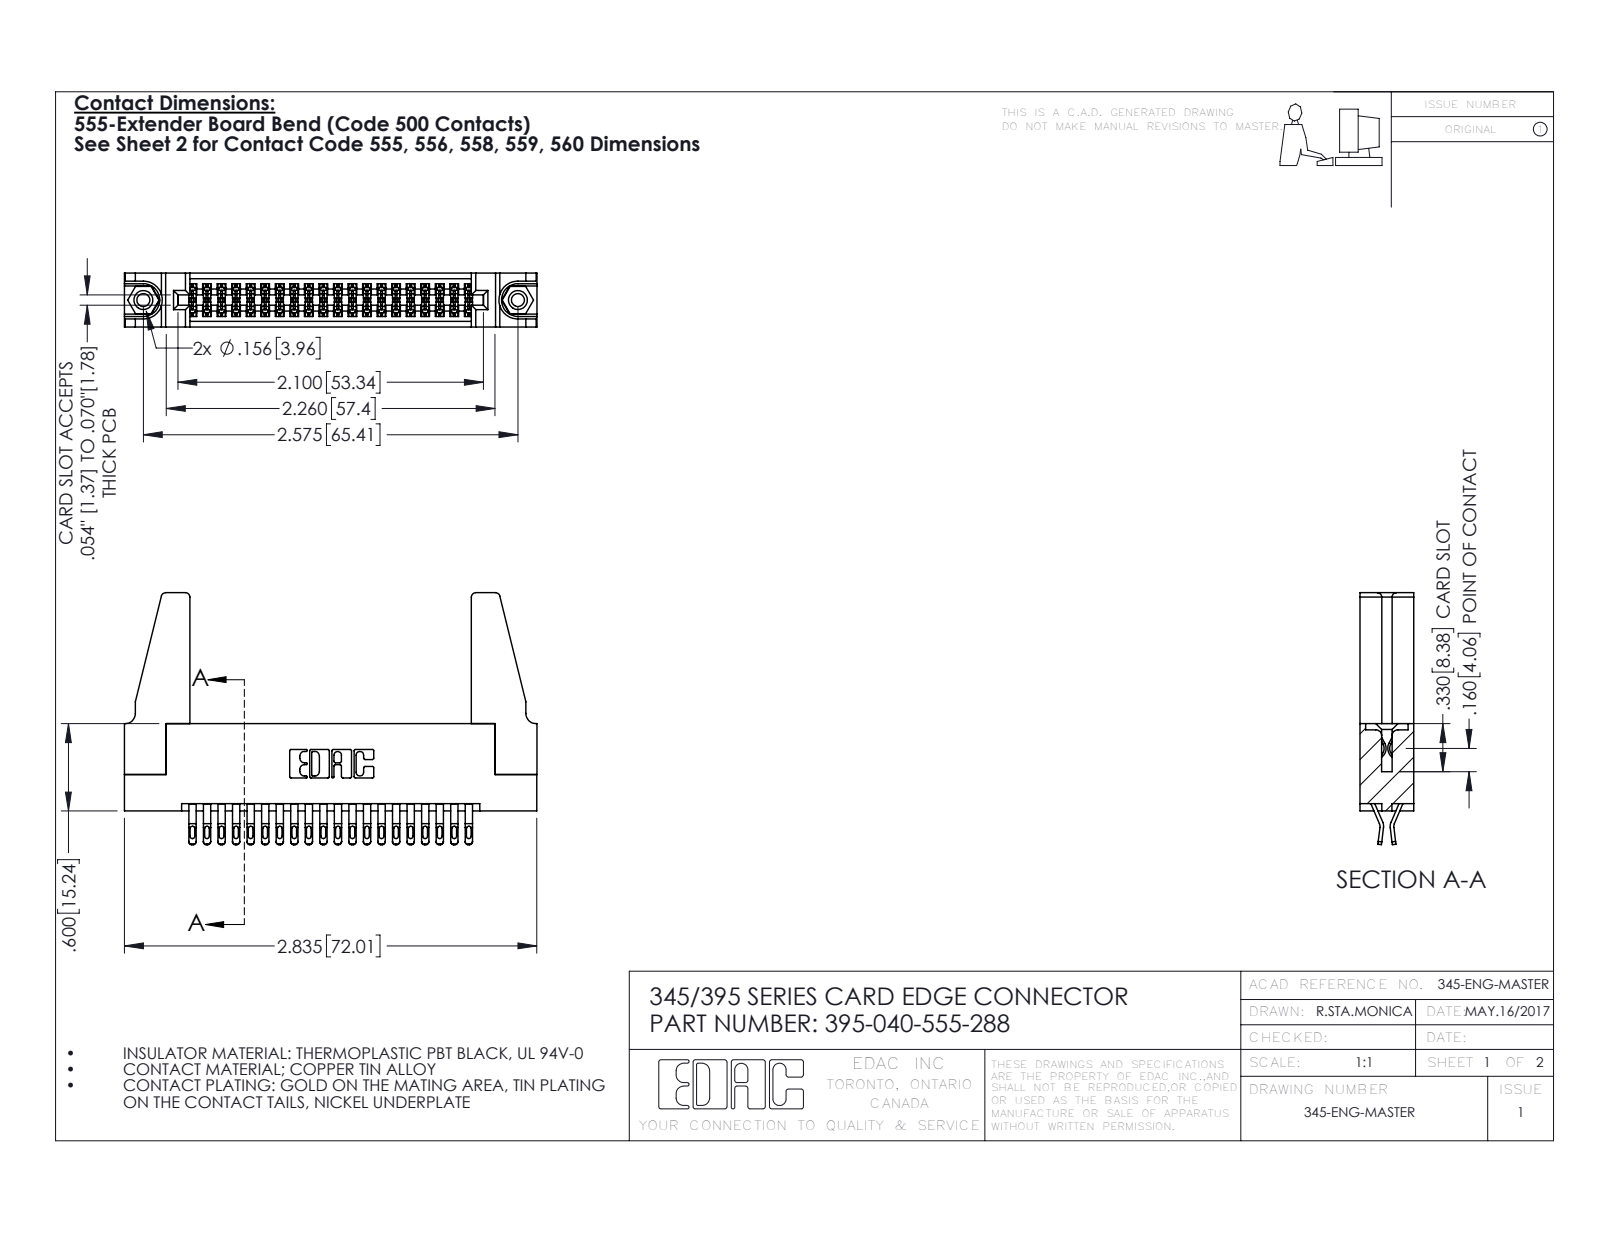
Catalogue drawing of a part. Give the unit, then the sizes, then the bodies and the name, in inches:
Units: inches
Overall size (bounding box): 2.836 × 1.732 × 0.37
Round holes (diameter × count): ⌀0.089 ×2, ⌀0.125 ×2, ⌀0.156 ×2, ⌀0.064 ×1
Round bosses / shafts (diameter × count): ⌀0.155 ×2
Partial cylindrical surfaces — rounded edges, fillets, slot ends (radius × count): R0.016 ×100, R0.02 ×80, R0.006 ×60, R0.01 ×22, R0.03 ×8, R0.007 ×6, R0.031 ×6, R0.026 ×3
Main face-to-face distances: 0.37, 0.072, 0.298, 0.2, 0.025, 0.098, 0.272, 0.225, 0.175, 0.149
Hole centre spacings: 0.27, 2.341, 2.575
Volume: 0.62 in³ · Surface area: 20.63 in²
Bodies: 45 solids, 2490 faces (1392 planar, 1082 cylindrical, 16 other)
Part name (STEP PRODUCT): 345-220-078_345-220-088; 345-292-001_555 Tail; 345-250-001_345-250-001-102; 395-040-555-288 (+1 more)
STEP written by: SolidWorks 2016 (CONFIG_CONTROL_DESIGN)
